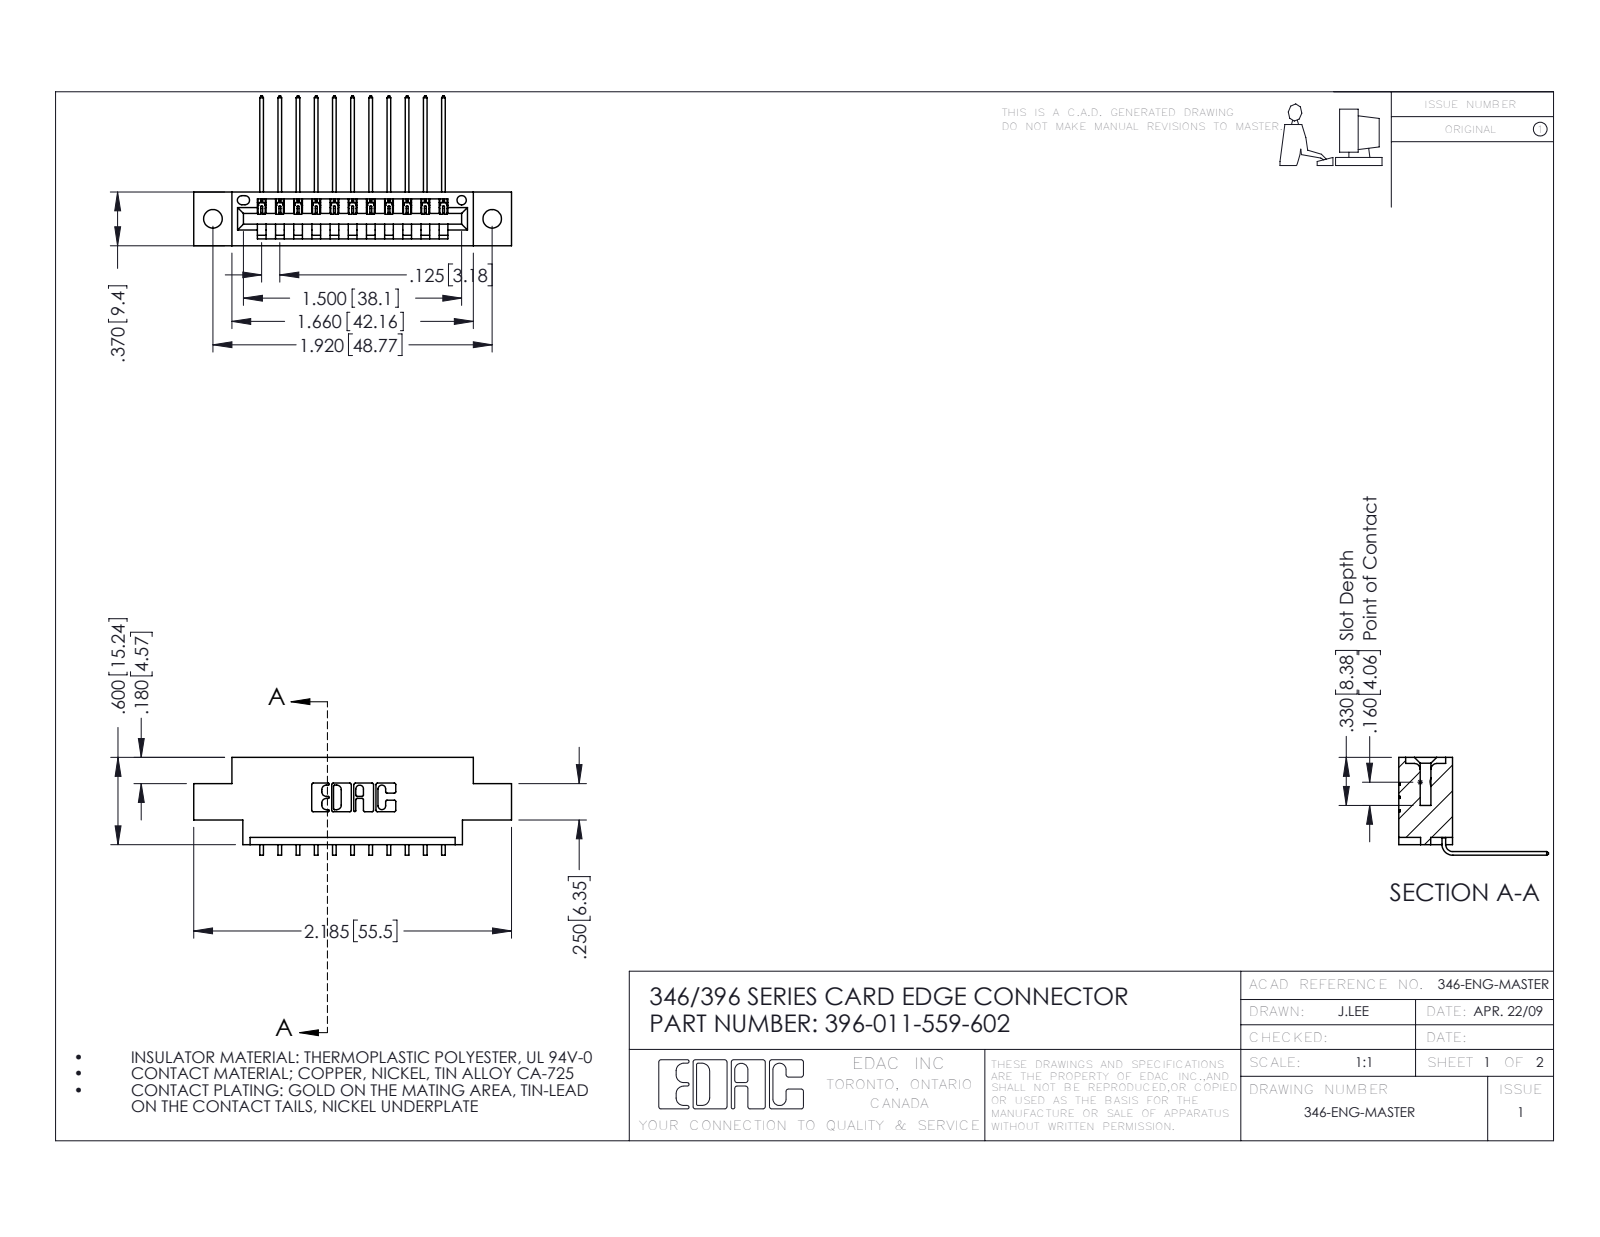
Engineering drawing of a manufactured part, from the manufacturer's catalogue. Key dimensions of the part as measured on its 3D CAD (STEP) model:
Part name (STEP PRODUCT): 345-292-001_558 559 Tail - 1; 396-011-559-602; 346 Part_0.170 Offset - 0.128 Dia
STEP written by: SolidWorks 2016 (CONFIG_CONTROL_DESIGN)
Units: inches
Bodies: 12 solids, 786 faces (542 planar, 244 cylindrical, 0 other)
Overall size (bounding box): 2.185 × 1.03 × 0.673
Volume: 0.302 in³ · Surface area: 9.227 in²
Round holes (diameter × count): ⌀0.128 ×2, ⌀0.064 ×1
Partial cylindrical surfaces — rounded edges, fillets, slot ends (radius × count): R0.006 ×22, R0.01 ×22, R0.007 ×6, R0.031 ×6, R0.026 ×3, R0.031 ×2, R0.04 ×2, R0.014 ×1
Main face-to-face distances: 0.25, 0.37, 0.048, 0.322, 0.025, 0.072, 0.148, 0.222, 0.1, 0.174
Hole centre spacings: 0.246, 1.715, 1.92
